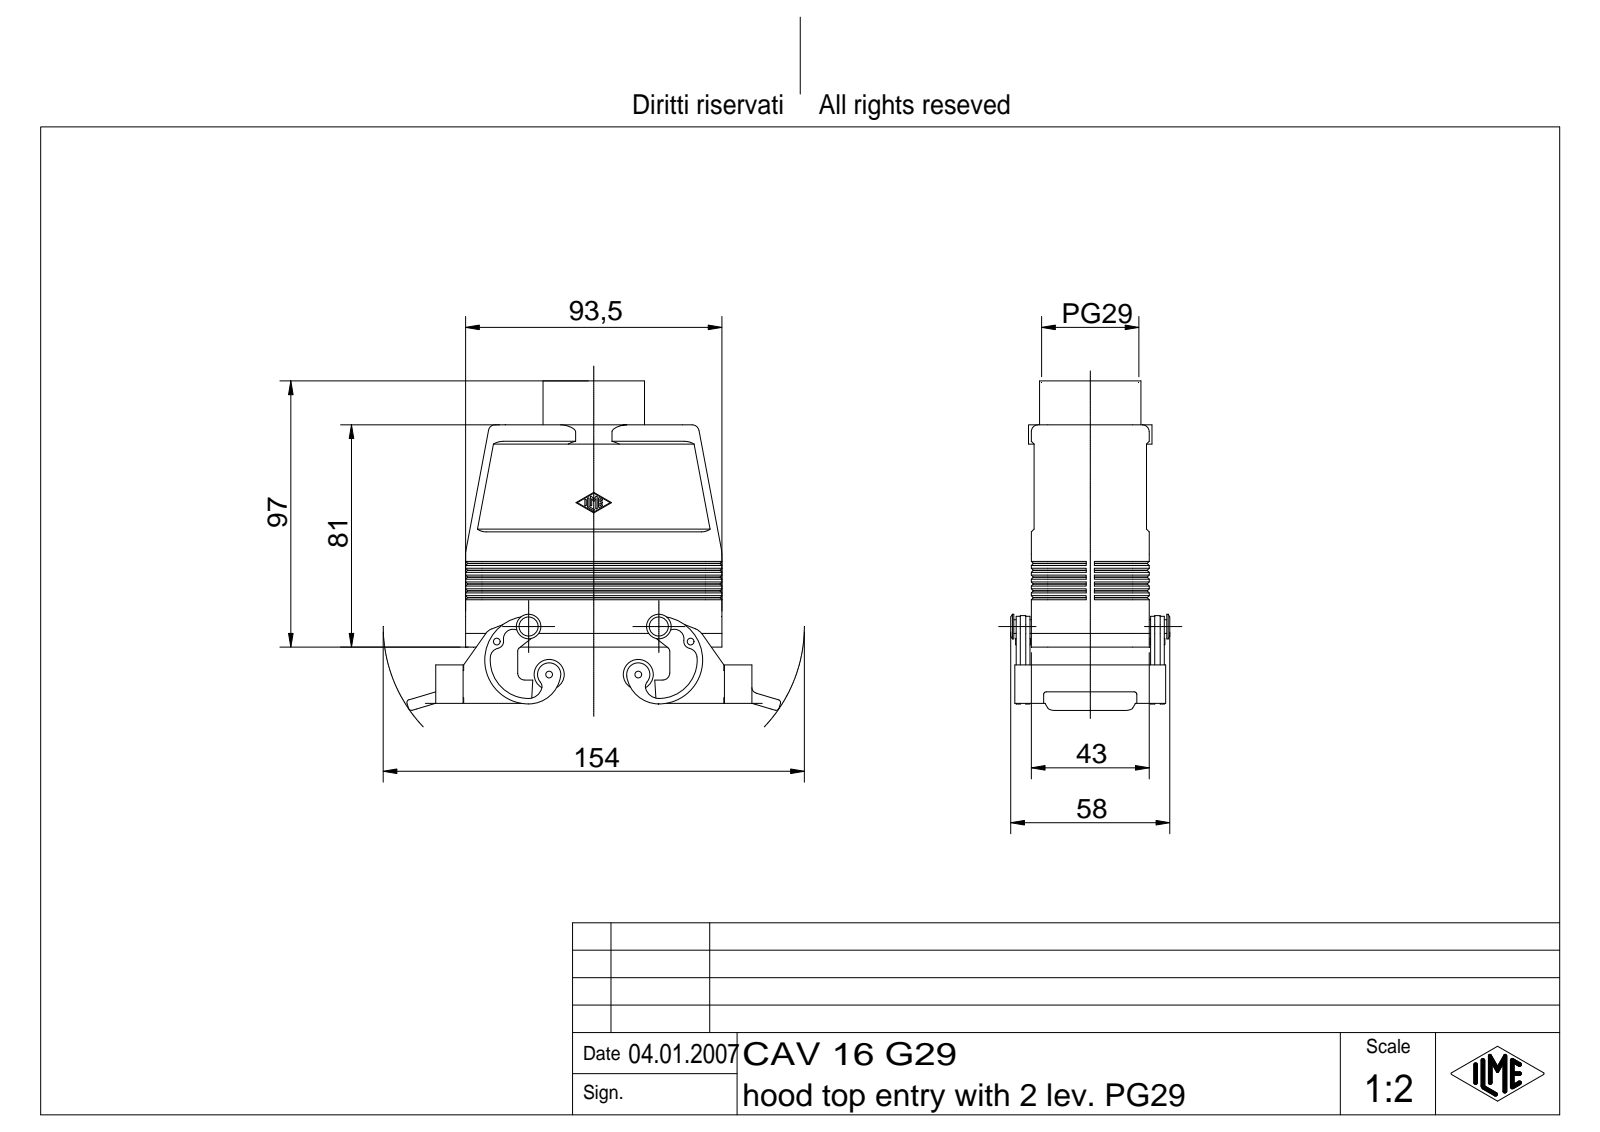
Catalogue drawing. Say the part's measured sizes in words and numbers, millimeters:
The part is named "CAV Tüllengehäuse 2 Bügel für einen Einsatz". Its 3-D file was written by "Autodesk Inventor 7 (AUTOMOTIVE_DESIGN)". It is 1 solid with 965 faces: 302 planar, 256 cylindrical and 407 other. Overall it measures 136.29 by 120.08 by 58 millimeters. Its volume is 109 647 cubic millimeters and its surface area 64 953 square millimeters. Round holes: 2 of diameter 2.5, 1 of diameter 33.48, 1 of diameter 35.48. Round bosses or shafts: 2 of diameter 11, 2 of diameter 9, 2 of diameter 5, 2 of diameter 2, 1 of diameter 45, 1 of diameter 37. Partial cylindrical surfaces (rounded edges, fillets, slot ends): 14 of radius 0.25, 12 of radius 1, 10 of radius 2.5, 10 of radius 6, 8 of radius 3, 7 of radius 2, 4 of radius 3.5, 4 of radius 5. The main face-to-face distances are 4, 3, 39, 35, 38, 1, 42, 43, 41, 2. The hole center spacings are 70.7.
